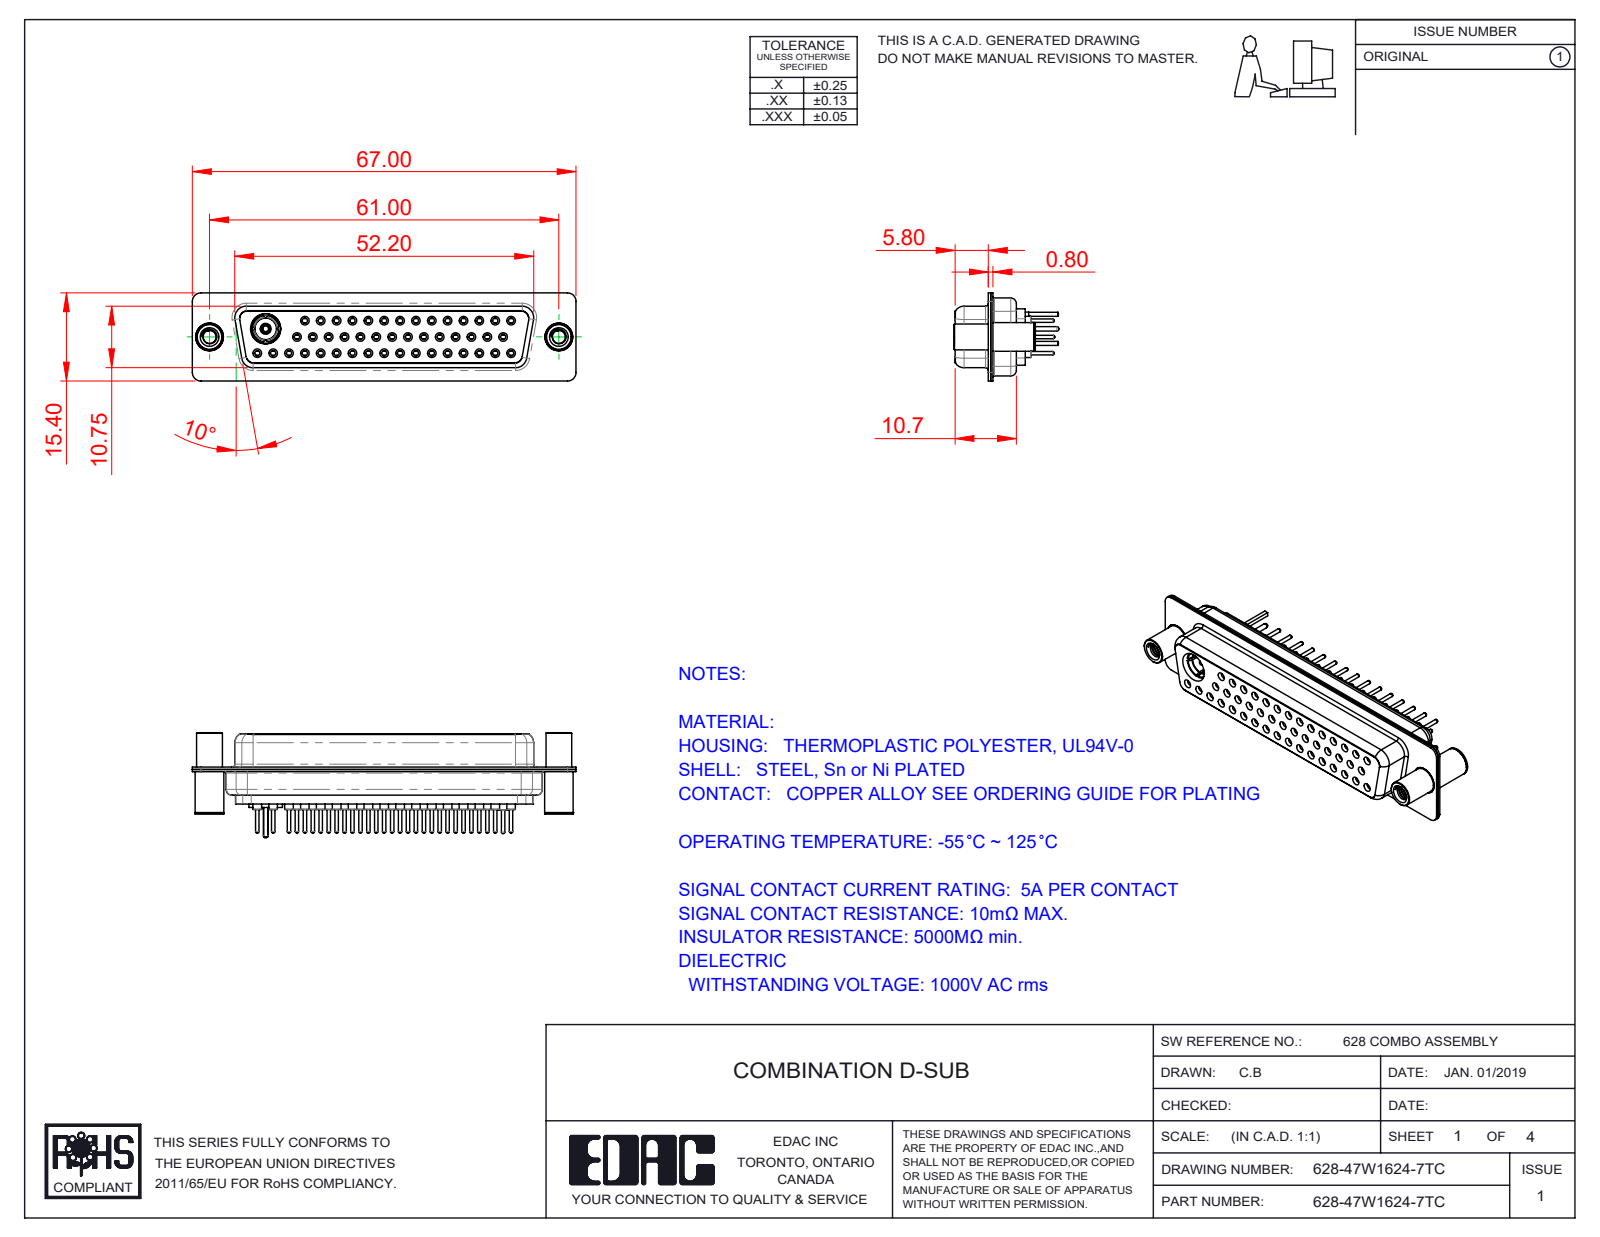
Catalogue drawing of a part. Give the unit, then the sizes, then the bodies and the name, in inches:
Units: inches
Overall size (bounding box): 2.638 × 0.722 × 0.606
Round holes (diameter × count): ⌀0.043 ×47, ⌀0.059 ×46, ⌀0.035 ×45, ⌀0.079 ×45, ⌀0.063 ×31, ⌀0.067 ×14, ⌀0.191 ×3, ⌀0.089 ×2, ⌀0.128 ×2, ⌀0.157 ×2, ⌀0.159 ×2, ⌀0.111 ×1
Round bosses / shafts (diameter × count): ⌀0.087 ×46, ⌀0.024 ×46, ⌀0.063 ×15, ⌀0.197 ×3, ⌀0.195 ×2, ⌀0.189 ×2, ⌀0.177 ×2, ⌀0.23 ×1
Partial cylindrical surfaces — rounded edges, fillets, slot ends (radius × count): R0.059 ×16, R0.053 ×12, R0.079 ×12, R0.063 ×8, R0.01 ×4, R0.02 ×4, R0.024 ×4, R0.026 ×4
Main face-to-face distances: 0.016, 0.238, 0.446, 0.254, 0.074, 0.482, 0.244, 0.228, 0.407, 0.43
Hole centre spacings: 0.124, 0.109, 0.218, 0.327, 0.436, 0.545, 0.654, 0.763
Volume: 0.448 in³ · Surface area: 23.88 in²
Bodies: 55 solids, 3027 faces (817 planar, 1120 cylindrical, 1090 other)
Part name (STEP PRODUCT): 628-47W1624-7TC; 628Combo Shell Front_50 Contacts; 628Combo Housing_47W1; Co-Ax Plug_Straight PC Tail (+8 more)
STEP written by: SolidWorks 2016 (CONFIG_CONTROL_DESIGN)
